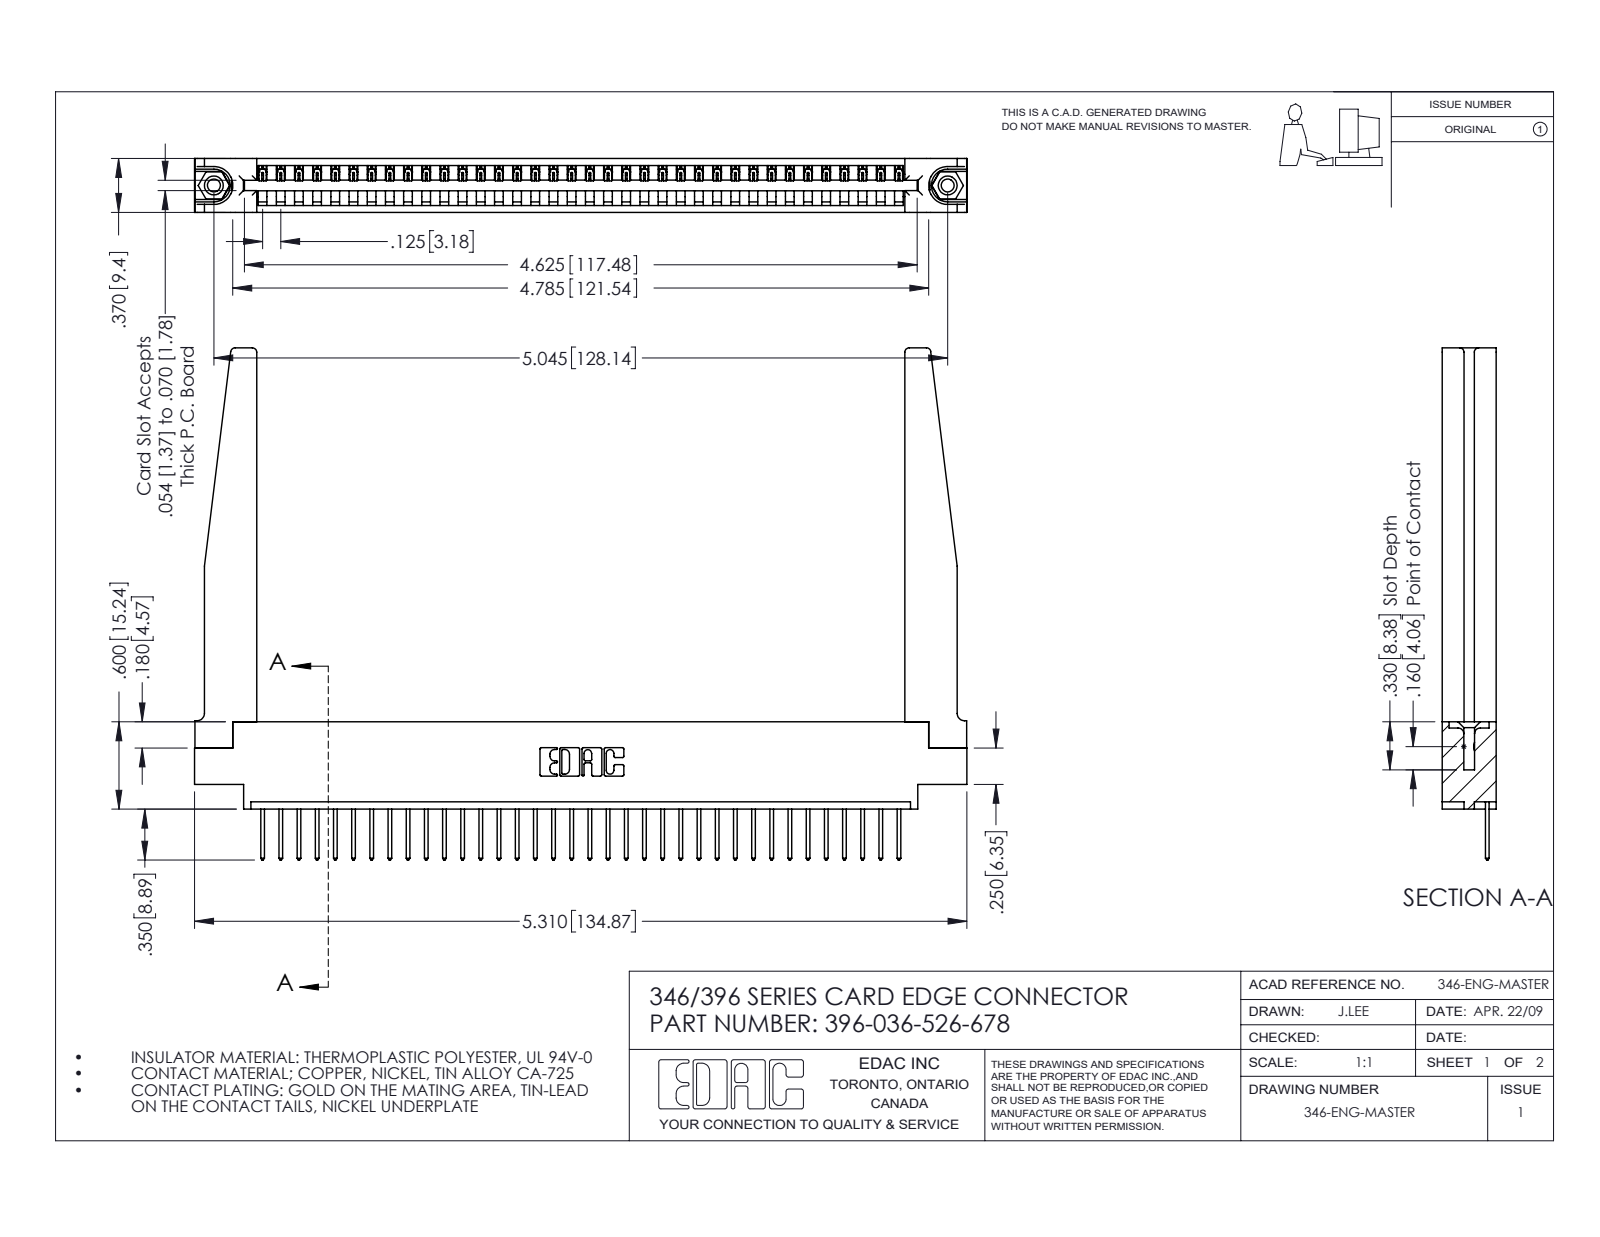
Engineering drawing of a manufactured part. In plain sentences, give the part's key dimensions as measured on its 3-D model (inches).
The part is named "346-220-078_345-220-078; 345-292-001_345-293-126; 396-036-526-678; 346 Part_0.170 Offset - 0.156 Dia-TH (+1 more)". Its 3-D file was written by "SolidWorks 2016 (CONFIG_CONTROL_DESIGN)". It is 41 solids with 2448 faces: 1662 planar, 734 cylindrical and 52 other. Overall it measures 5.31 by 3.52 by 0.37 inches. Its volume is 1.196 cubic inches and its surface area 34.81 square inches. Round holes: 2 of diameter 0.089, 2 of diameter 0.125, 2 of diameter 0.156, 1 of diameter 0.064. Round bosses or shafts: 2 of diameter 0.155. Partial cylindrical surfaces (rounded edges, fillets, slot ends): 72 of radius 0.006, 72 of radius 0.01, 22 of radius 0.01, 8 of radius 0.03, 6 of radius 0.007, 6 of radius 0.031, 3 of radius 0.026, 2 of radius 0.031. The main face-to-face distances are 0.37, 0.048, 0.322, 0.072, 0.148, 0.15, 0.25, 0.298, 0.025, 0.222. The hole center spacings are 0.246, 4.836, 5.045.
